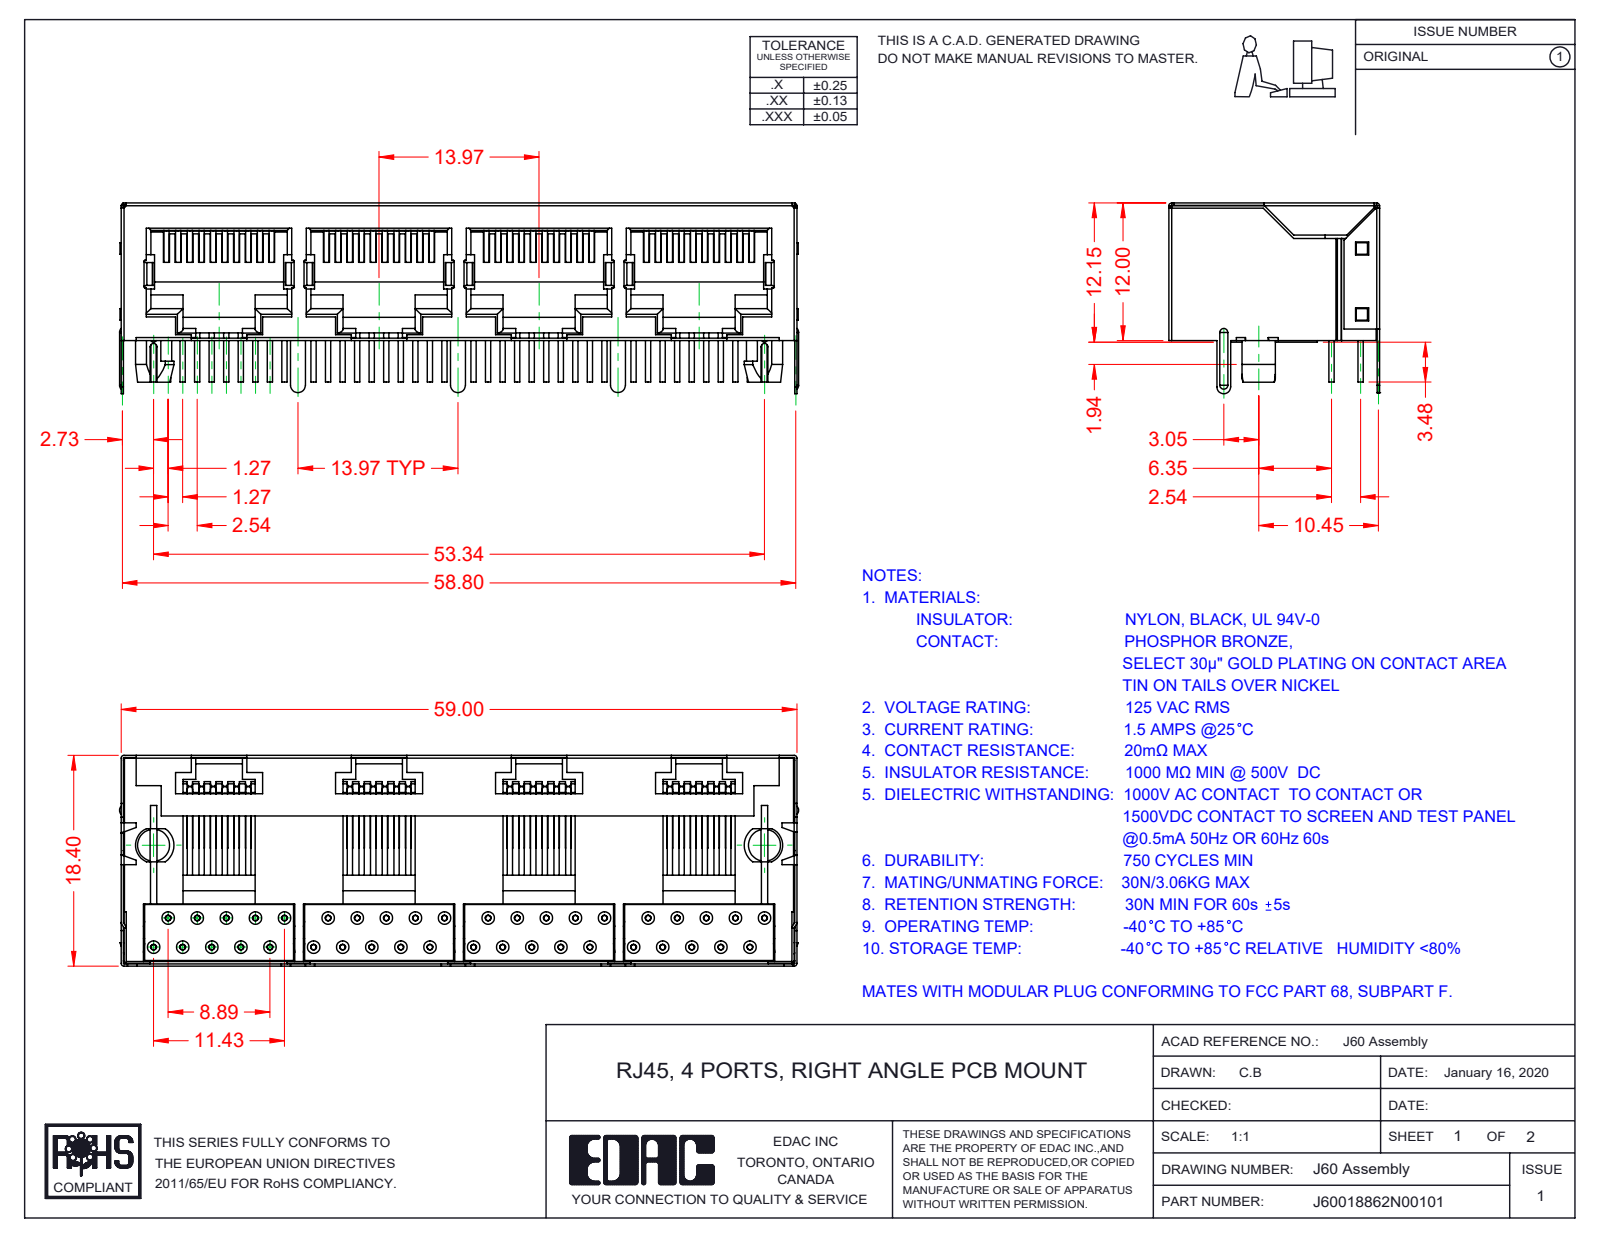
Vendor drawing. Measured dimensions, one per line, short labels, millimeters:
name: RJ60041162N00101; 60 Insulator; 60 Contacts_10P10C; 60 Shield
written by: SolidWorks 2016 (CONFIG_CONTROL_DESIGN)
unit: mm
bodies: 42 solids, 2674 faces (1505 planar, 763 cylindrical, 406 other)
size: 59.3 × 18.4 × 16.65
volume: 7 062 mm³; area: 18 987 mm²
holes: 40× ⌀0.5, 40× ⌀1.1
bosses: 120× ⌀0.46
rounds: 26× R0.3, 21× R0.25, 18× R0.5, 16× R0.1, 10× R0.21, 7× R0.8, 3× R0.65, 2× R0.28
face distances: 0.5, 11.75, 11.55, 13.97, 2.19, 5.38, 5.18, 4.88, 18.2, 11.5
hole spacings: 2.84, 2.54, 4.58, 13.97, 5.08, 12.95, 15.45, 11.43
